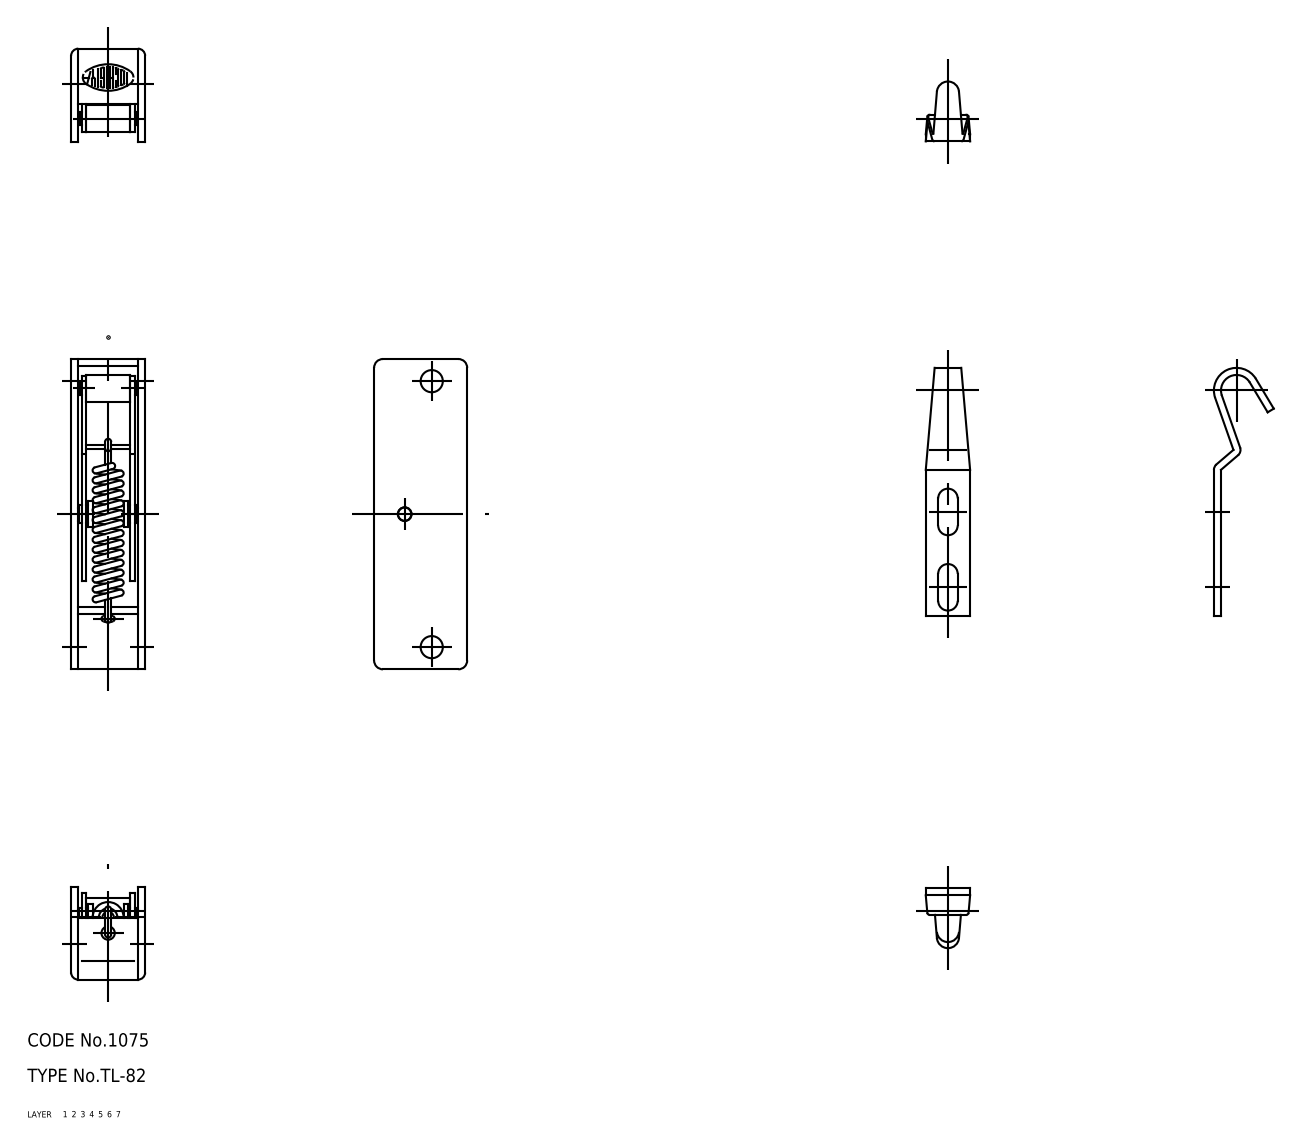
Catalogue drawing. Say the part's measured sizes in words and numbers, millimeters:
The part is named "spring; keeper; shaft; roller (+5 more)". Its 3-D file was written by "CADfix (AUTOMOTIVE_DESIGN)". It is 8 solids with 205 faces: 0 planar, 0 cylindrical and 205 other. Overall it measures 70 by 42.9 by 16.7 millimeters. Its volume is 9 448 cubic millimeters and its surface area 14 634 square millimeters.
